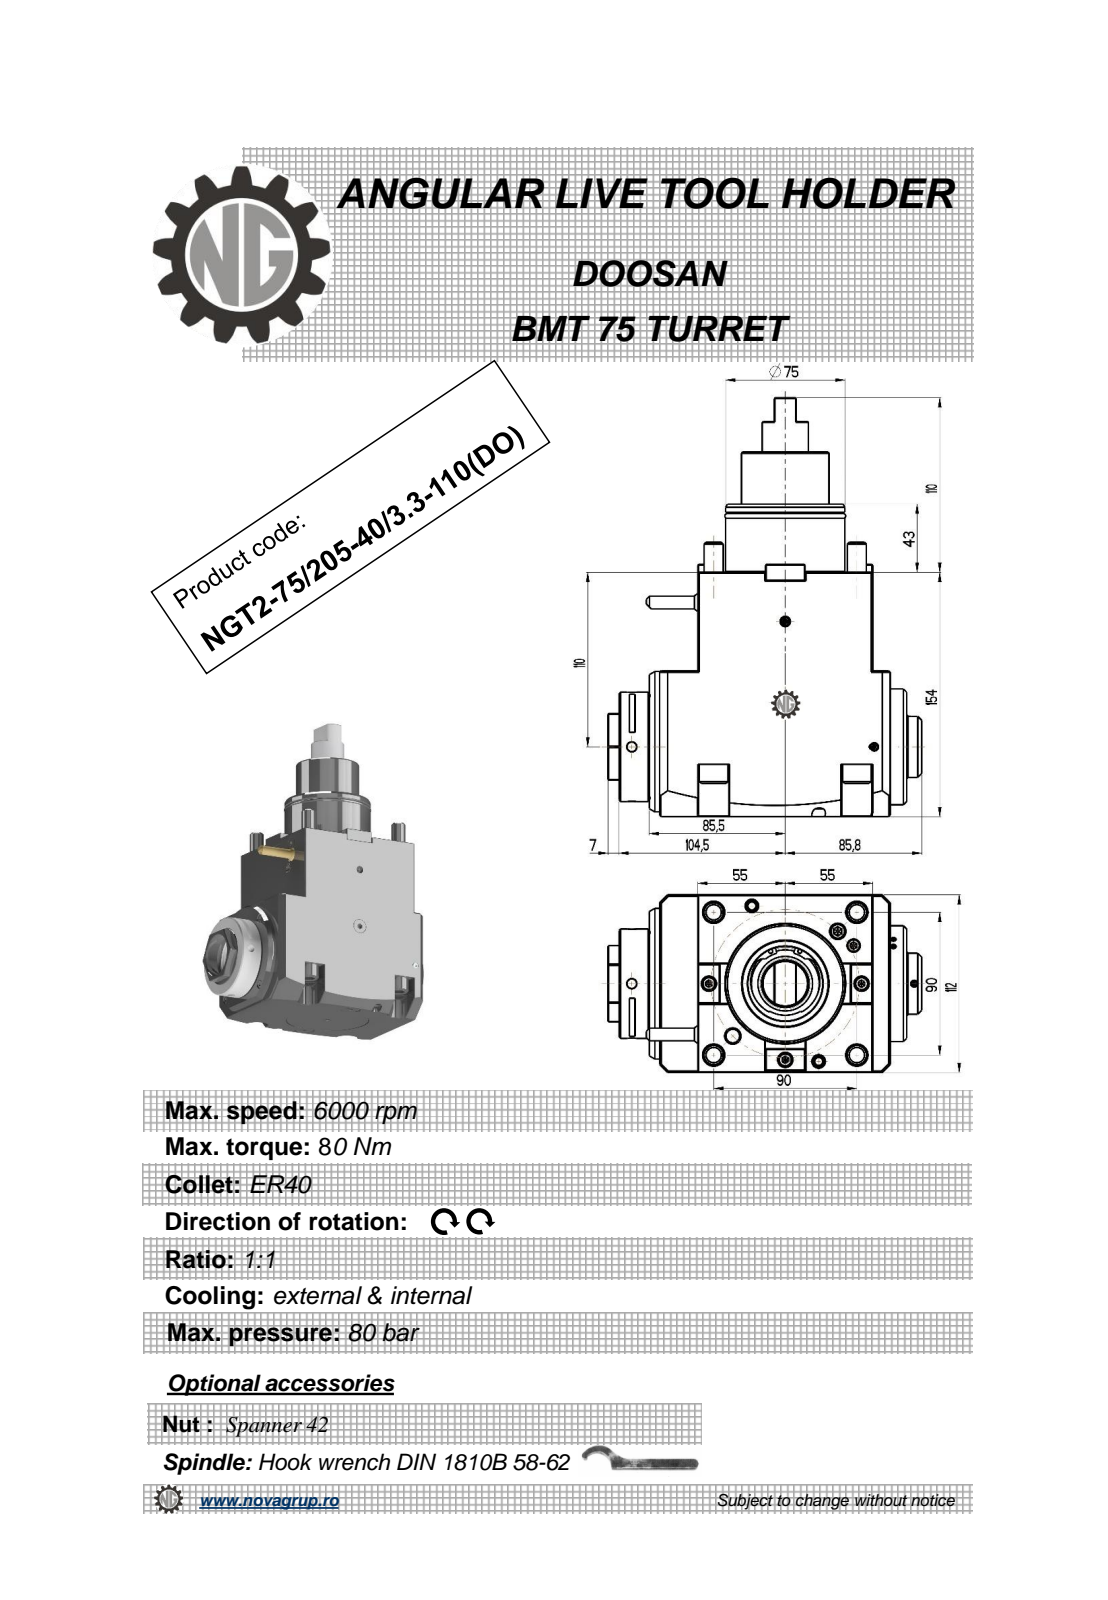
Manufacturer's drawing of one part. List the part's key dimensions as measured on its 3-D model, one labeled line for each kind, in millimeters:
Part name (STEP PRODUCT): NGT2_75_205_40_3_3_110_DO
STEP written by: PRO/ENGINEER BY PARAMETRIC TECHNOLOGY CORPORATION, 2010280 (CONFIG_CONTROL_DESIGN)
Units: millimetres
Bodies: 2 solids, 308 faces (152 planar, 75 cylindrical, 81 other)
Overall size (bounding box): 264 × 197.3 × 112
Volume: 2 671 000 mm³ · Surface area: 151 701 mm²
Round holes (diameter × count): ⌀6 ×2, ⌀8.5 ×2, ⌀3 ×1, ⌀5 ×1, ⌀36.2 ×1
Round bosses / shafts (diameter × count): ⌀18 ×4, ⌀12 ×4, ⌀95 ×1, ⌀75 ×1, ⌀74 ×1, ⌀73 ×1, ⌀70 ×1, ⌀69 ×1
Partial cylindrical surfaces — rounded edges, fillets, slot ends (radius × count): R9.5 ×4, R0.8 ×2, R350 ×2, R24 ×1
Main face-to-face distances: 112, 110, 154, 121, 11, 62, 92, 30.5, 140.5, 19
Hole centre spacings: 71.56, 93.34, 96.46, 133.64
